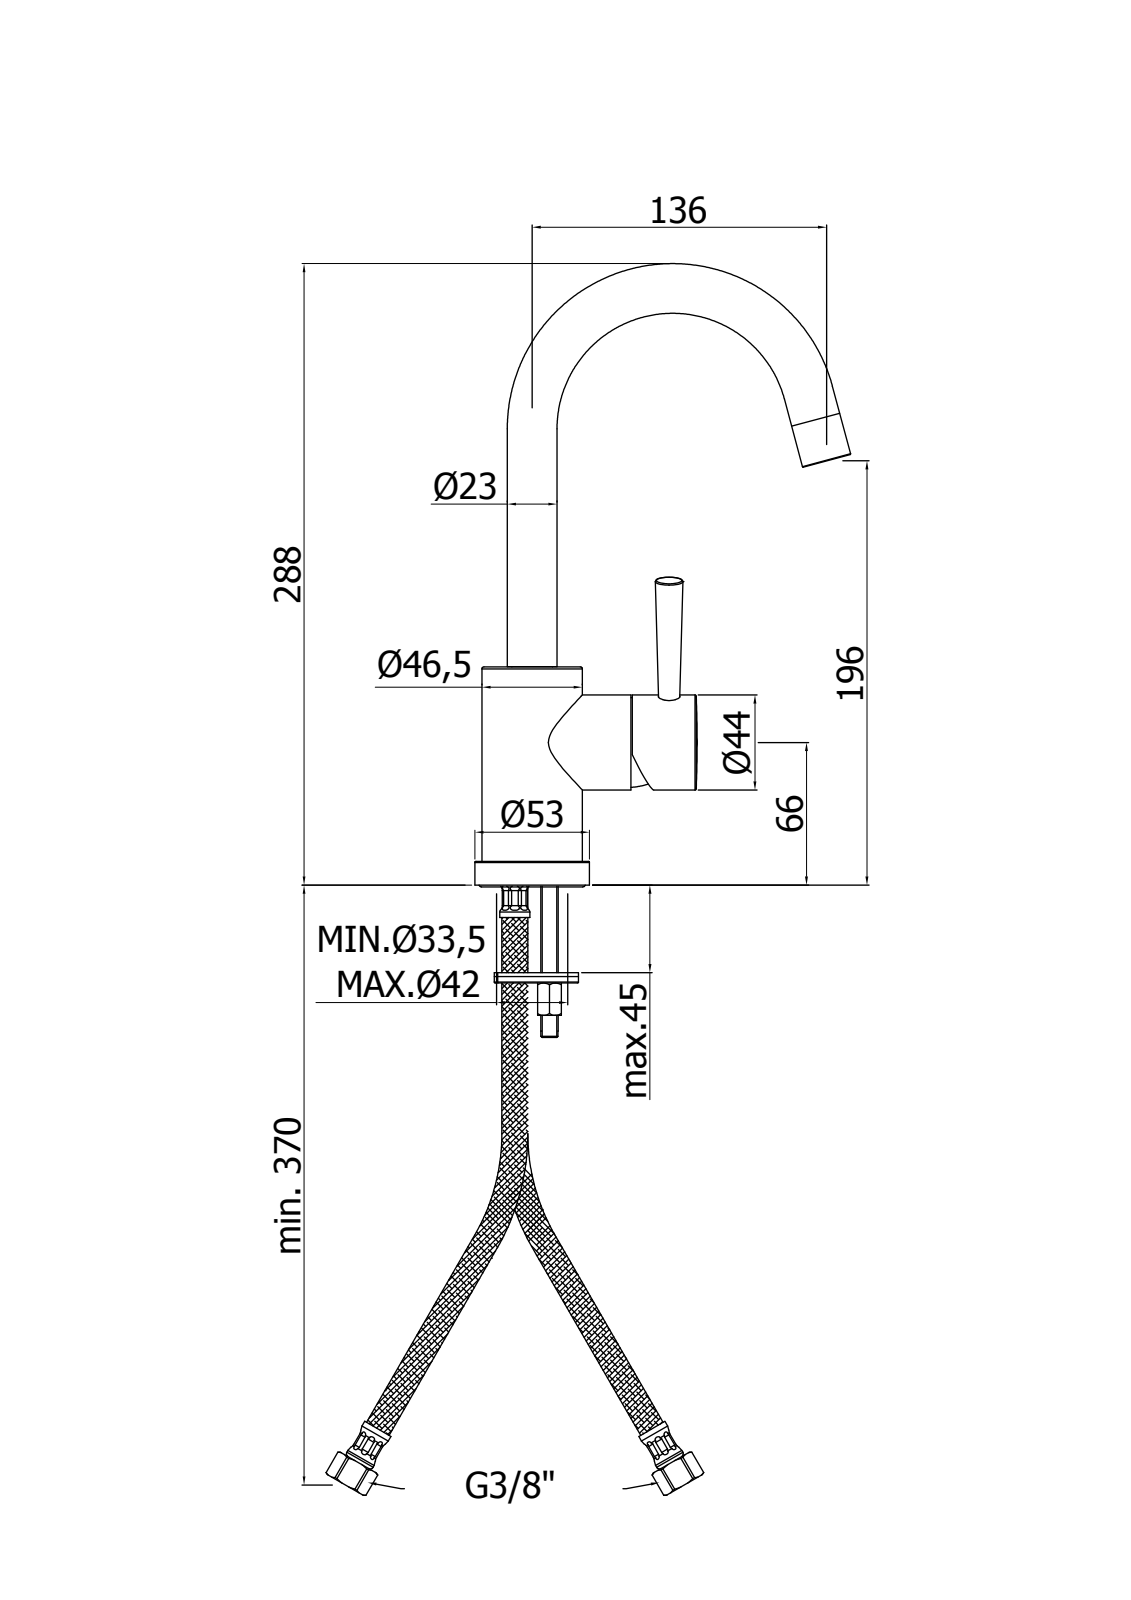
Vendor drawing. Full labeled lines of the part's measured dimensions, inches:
Part name (STEP PRODUCT): BI078CR
STEP written by: CREO PARAMETRIC BY PTC INC, 2020044 (CONFIG_CONTROL_DESIGN)
Units: inches
Bodies: 4 solids, 240 faces (61 planar, 109 cylindrical, 70 other)
Overall size (bounding box): 11.323 × 6.829 × 4.108
Volume: 11.92 in³ · Surface area: 161.6 in²
Round holes (diameter × count): ⌀0.256 ×3, ⌀0.354 ×3, ⌀0.197 ×2, ⌀0.217 ×2, ⌀0.433 ×2, ⌀0.748 ×2, ⌀1.575 ×2, ⌀0.118 ×1, ⌀0.13 ×1, ⌀0.268 ×1, ⌀0.394 ×1, ⌀0.591 ×1
Round bosses / shafts (diameter × count): ⌀0.906 ×3, ⌀2.087 ×1, ⌀1.831 ×1, ⌀1.732 ×1, ⌀1.681 ×1, ⌀0.866 ×1, ⌀0.768 ×1, ⌀0.74 ×1
Partial cylindrical surfaces — rounded edges, fillets, slot ends (radius × count): R0.197 ×1, R0.916 ×1
Main face-to-face distances: 3.975, 3.976, 2.406, 1.024, 1.022, 2.953, 0.512, 1.782, 0.623, 0.433
Hole centre spacings: 0.406, 0.432, 0.804, 0.047, 0.197, 0.361, 0.365, 0.401
